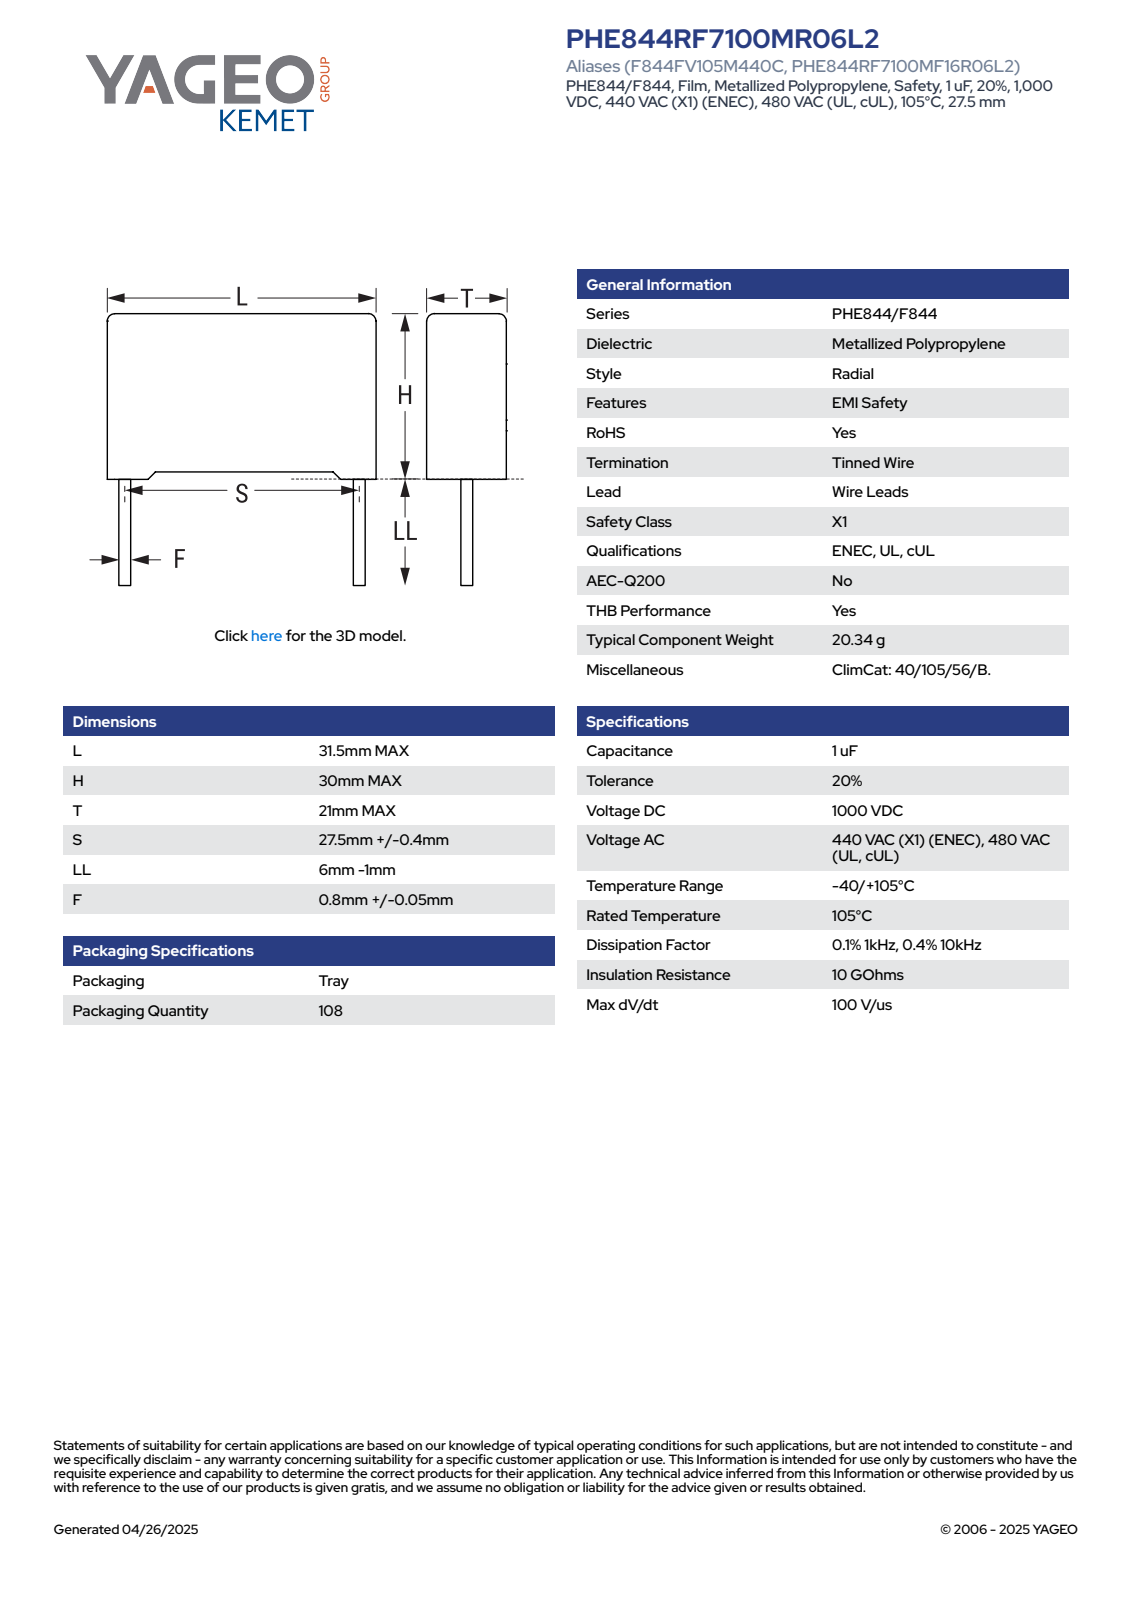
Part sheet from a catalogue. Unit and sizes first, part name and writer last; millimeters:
Units: millimetres
Overall size (bounding box): 35 × 31.5 × 21
Round bosses / shafts (diameter × count): ⌀0.85 ×2
Partial cylindrical surfaces — rounded edges, fillets, slot ends (radius × count): R0.5 ×4
Main face-to-face distances: 21, 31.5, 28.97, 29.25, 0.75, 1.03, 30, 1.05, 30.45, 21.01
Volume: 19 254 mm³ · Surface area: 4 550 mm²
Bodies: 4 solids, 85 faces (77 planar, 8 cylindrical, 0 other)
Part name (STEP PRODUCT): CFR_RB2_31.5X30X21_L31.5H30T21S27.5LL5F0.85
STEP written by: SolidWorks 2021 (AUTOMOTIVE_DESIGN)
